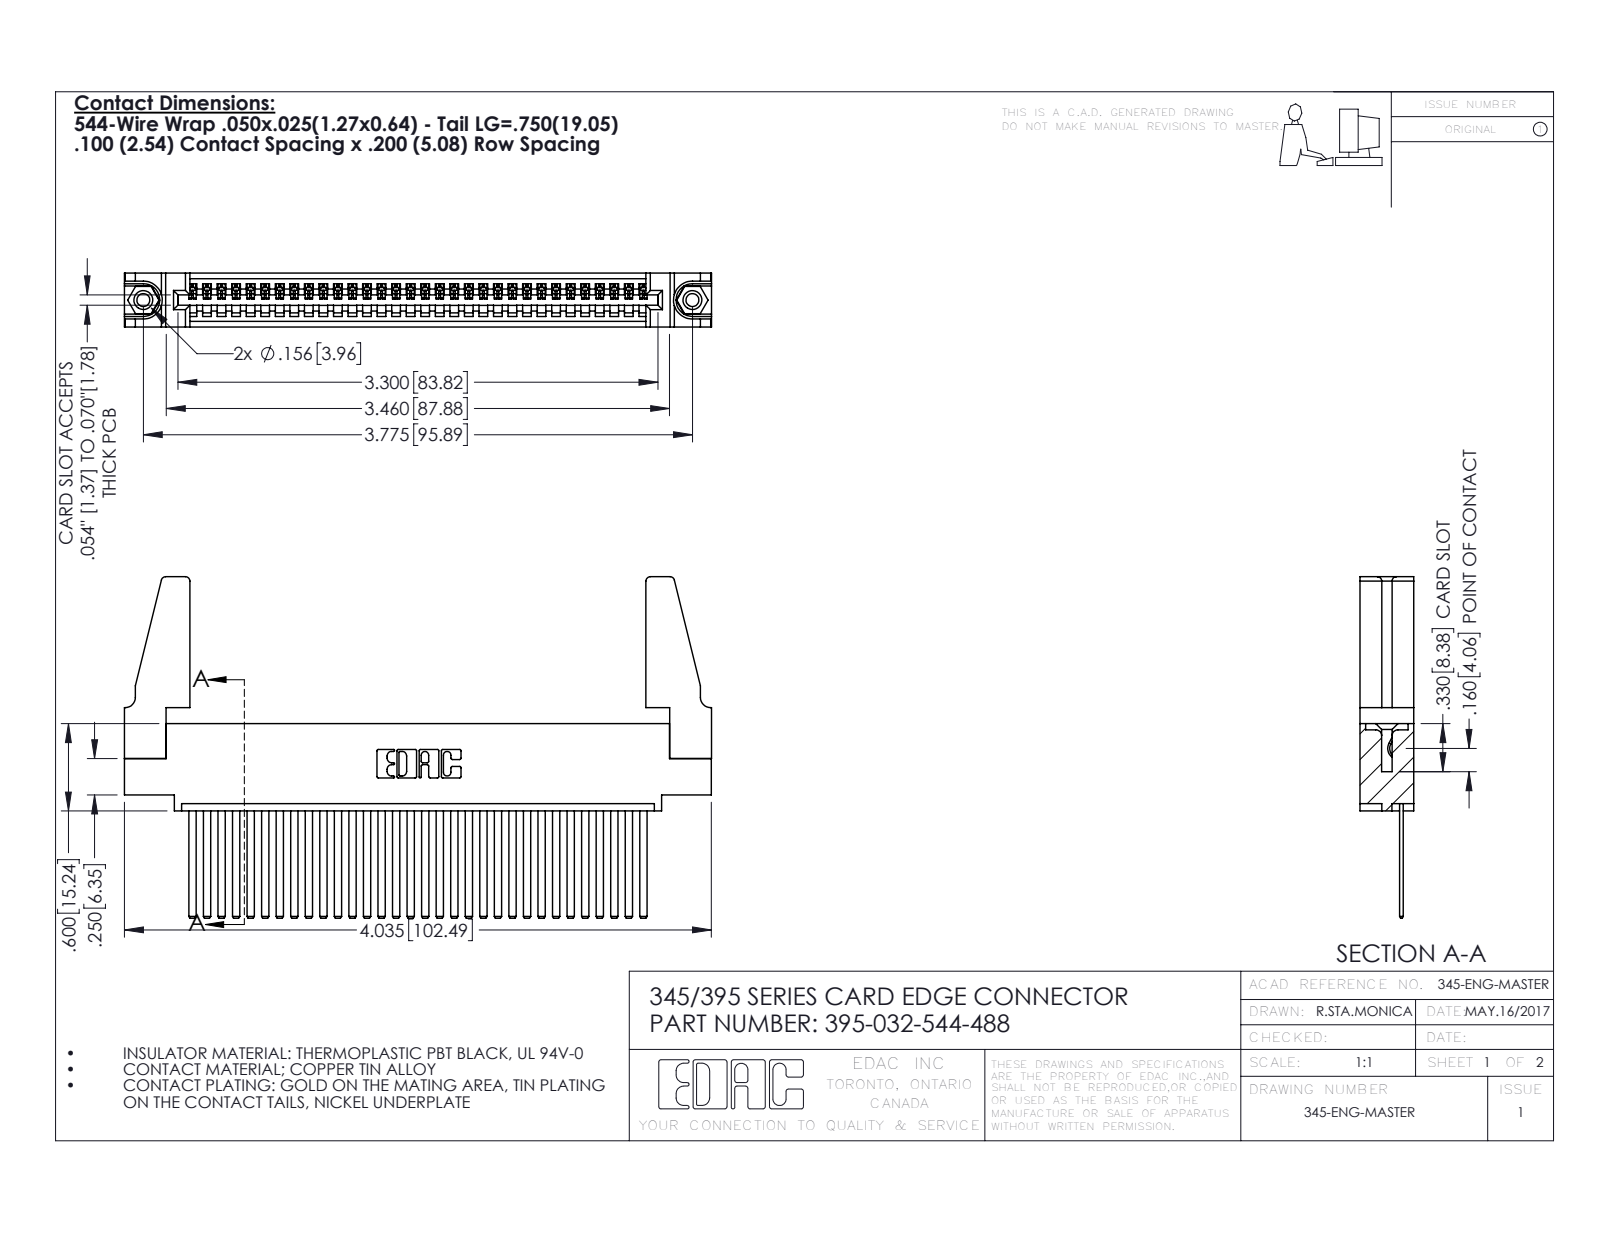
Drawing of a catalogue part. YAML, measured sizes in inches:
part_name: "345 Part_0.110 Offset - 0.156 Dia-TH; 345-220-078_345-220-088; 395-032-544-488; 345-292-001_345-293-144 (+1 more)"
step_written_by: "SolidWorks 2016 (CONFIG_CONTROL_DESIGN)"
units: inches
bodies: {solids: 37, faces: 1918, planar: 1308, cylindrical: 594, other: 16}
overall_size: [4.036, 2.347, 0.37]
volume: 0.806
surface_area: 26.99
round_holes:
  - {diameter: 0.089, count: 2}
  - {diameter: 0.125, count: 2}
  - {diameter: 0.156, count: 2}
  - {diameter: 0.064, count: 1}
round_bosses_or_shafts:
  - {diameter: 0.155, count: 2}
partial_cylinders:
  - {radius: 0.006, count: 64}
  - {radius: 0.01, count: 22}
  - {radius: 0.03, count: 8}
  - {radius: 0.007, count: 6}
  - {radius: 0.031, count: 6}
  - {radius: 0.026, count: 3}
  - {radius: 0.031, count: 2}
  - {radius: 0.04, count: 2}
face_to_face_distances: [0.072, 0.298, 0.37, 0.098, 0.272, 0.025, 0.2, 0.225, 0.149, 0.072]
hole_center_spacings: [0.27, 3.54, 3.775]
